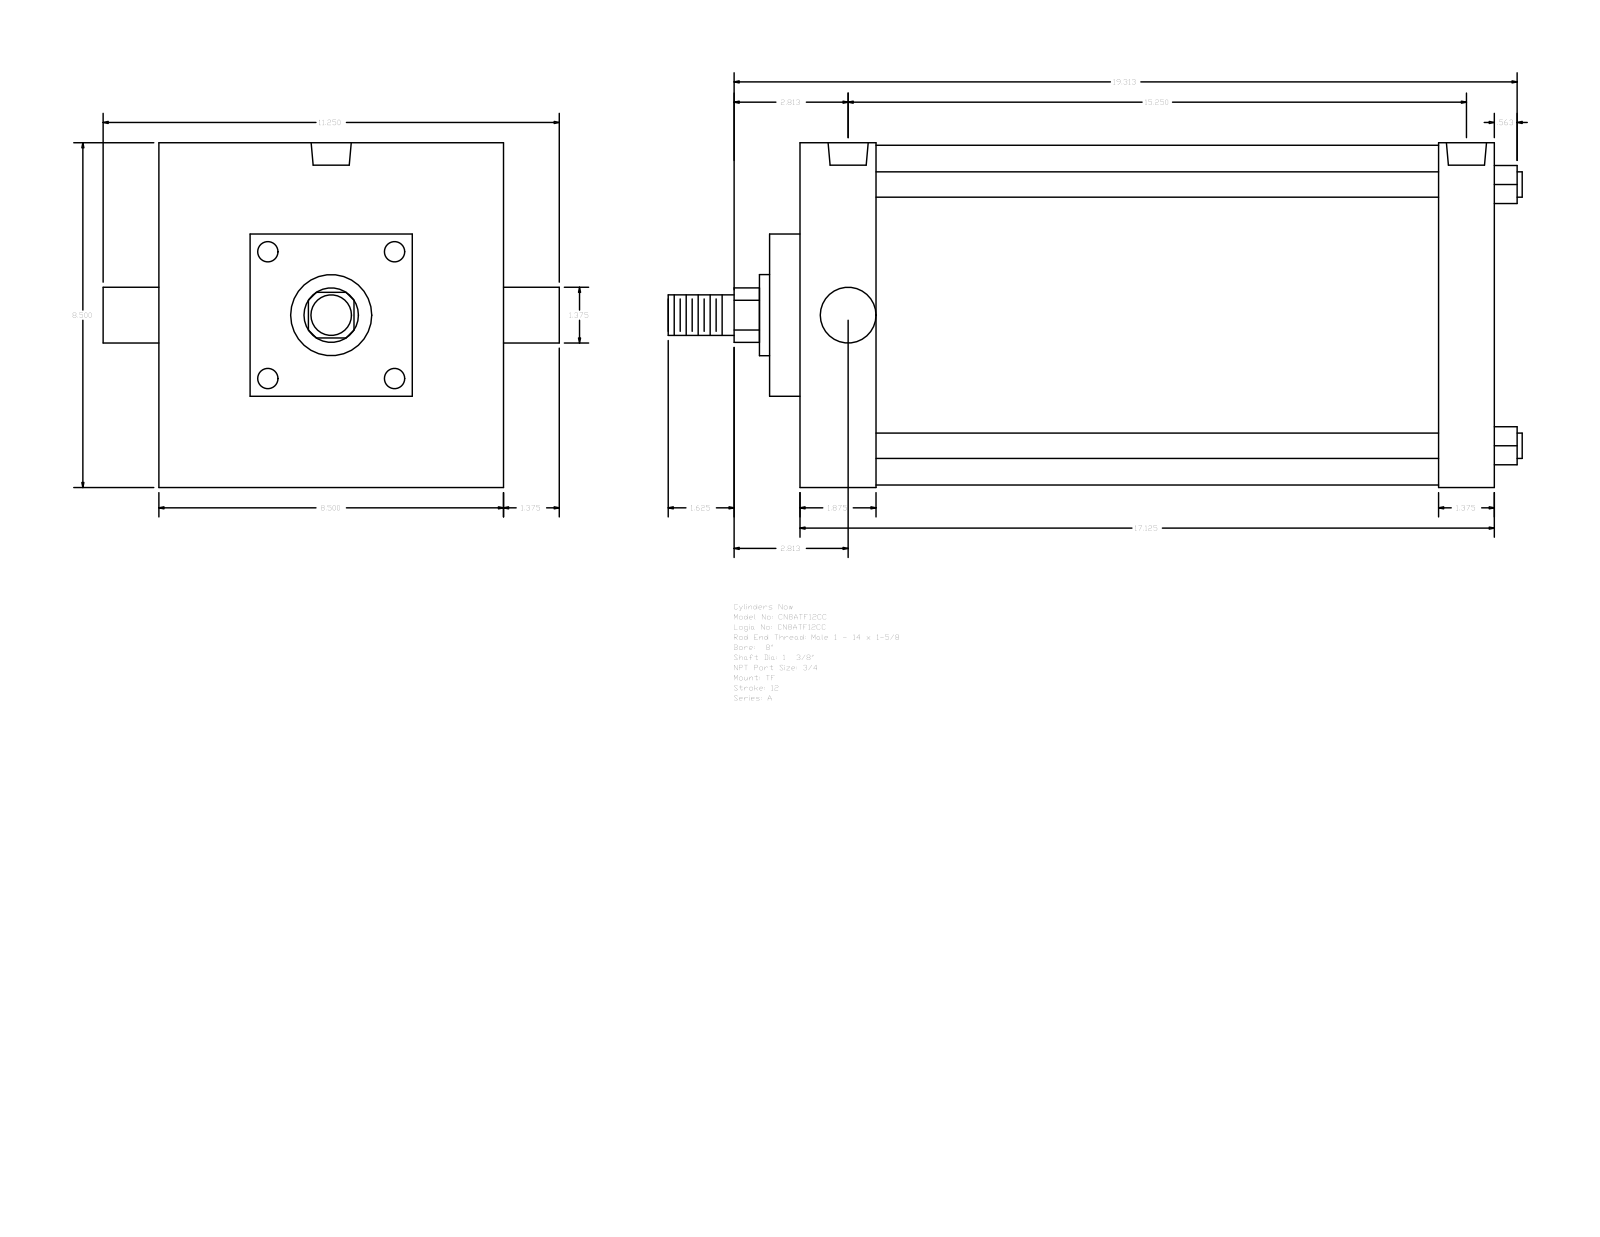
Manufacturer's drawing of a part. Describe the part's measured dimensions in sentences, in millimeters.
The part is named "A_TF__0800_1.375". Its 3-D file was written by "GSSL Pune (CONFIG_CONTROL_DESIGN)". It is 0 solids with 89 faces: 65 planar, 24 cylindrical and 0 other. Overall it measures 534.99 by 285.75 by 215.9 millimeters. Round holes: 3 of diameter 15.08, 2 of diameter 25.12. Round bosses or shafts: 4 of diameter 15.88, 2 of diameter 34.92, 1 of diameter 212.72, 1 of diameter 50.8, 1 of diameter 25.4. Partial cylindrical surfaces (rounded edges, fillets, slot ends): 1 of radius 17.06. The main face-to-face distances are 434.98, 215.9, 34.93, 47.63, 387.35, 400.05, 352.42, 19.04, 66.67, 419.09. The hole center spacings are 6.35, 381, 374.65, 387.35.
